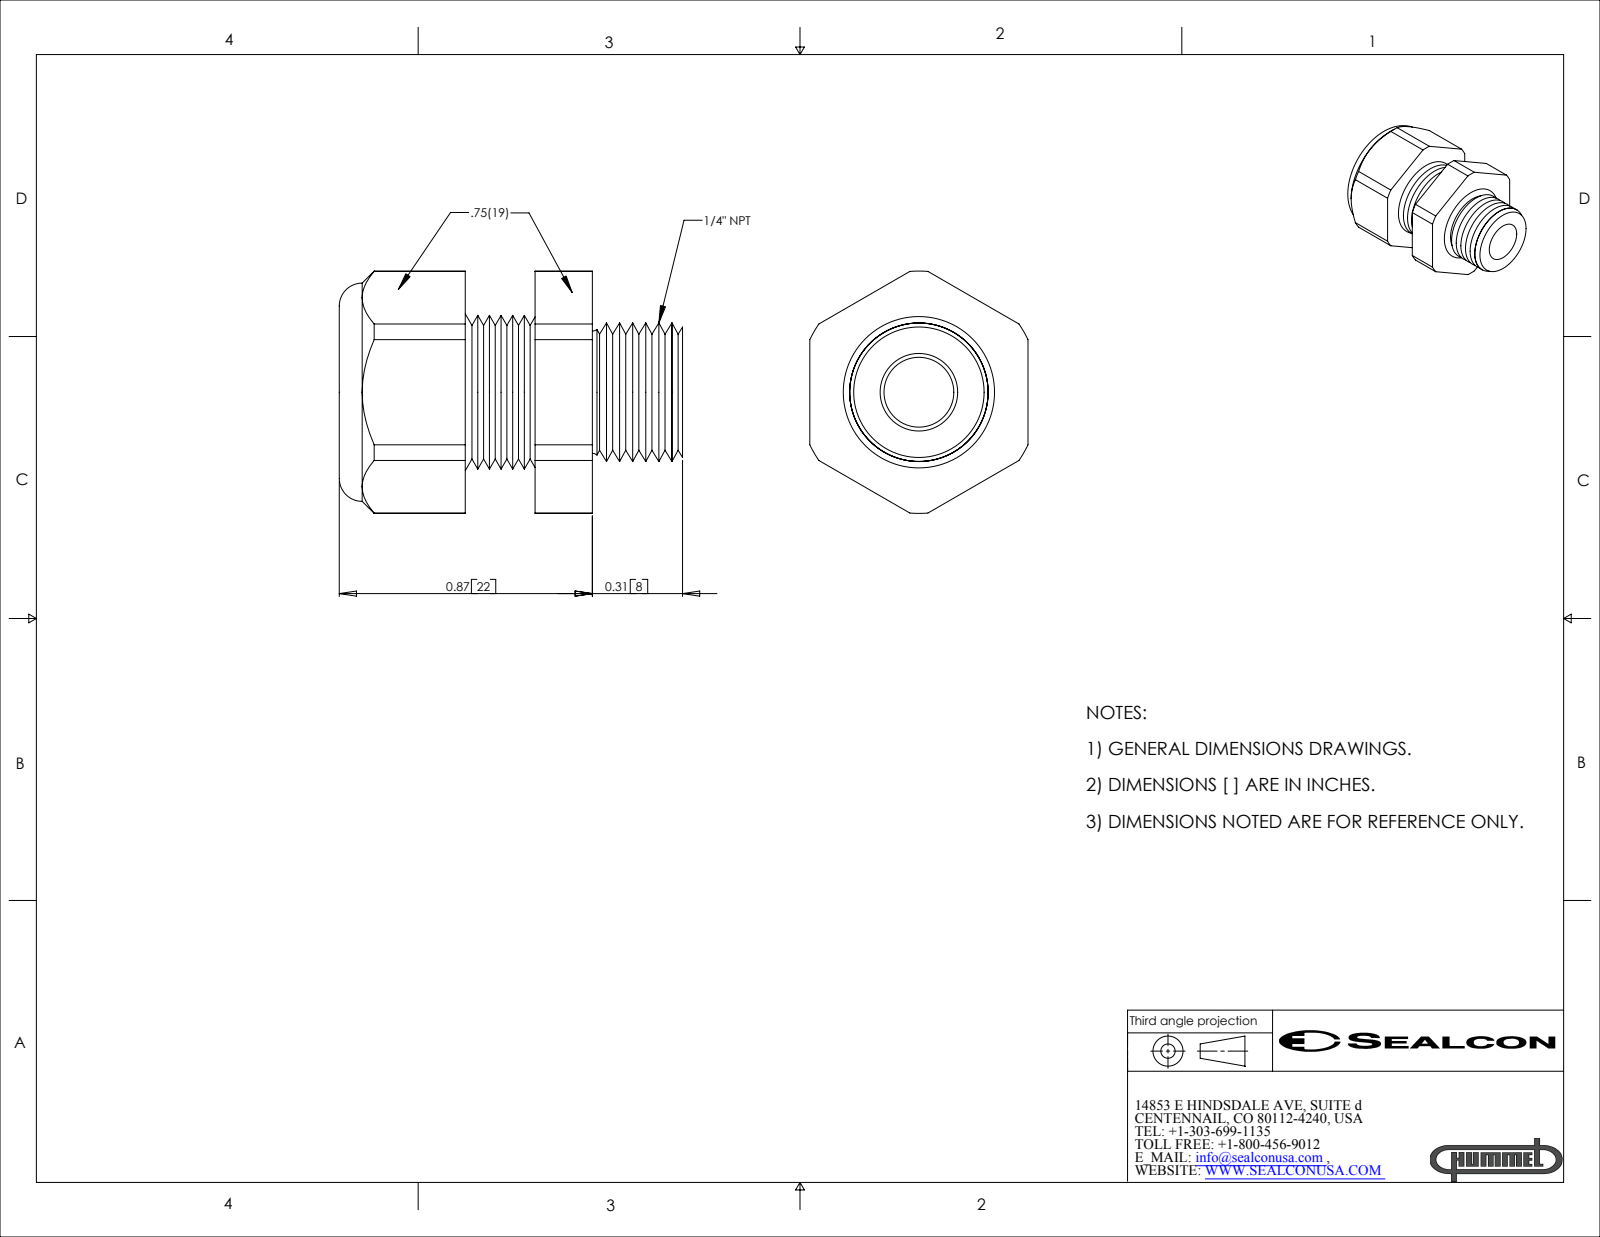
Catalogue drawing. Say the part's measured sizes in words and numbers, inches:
The part is named "CD07GR-GY". Its 3-D file was written by "SolidWorks 2007 (CONFIG_CONTROL_DESIGN)". It is 2 solids with 112 faces: 20 planar, 22 cylindrical and 70 other. Overall it measures 1.18 by 0.833 by 0.75 inches. Its volume is 0.328 cubic inches and its surface area 6.967 square inches. Round holes: 1 of diameter 0.24, 1 of diameter 0.49, 1 of diameter 0.539. Partial cylindrical surfaces (rounded edges, fillets, slot ends): 1 of radius 0.416. The main face-to-face distances are 0.75, 0.437, 0.24, 0.197, 0.75, 0.403, 0.643, 0.84, 1.15, 0.747.
